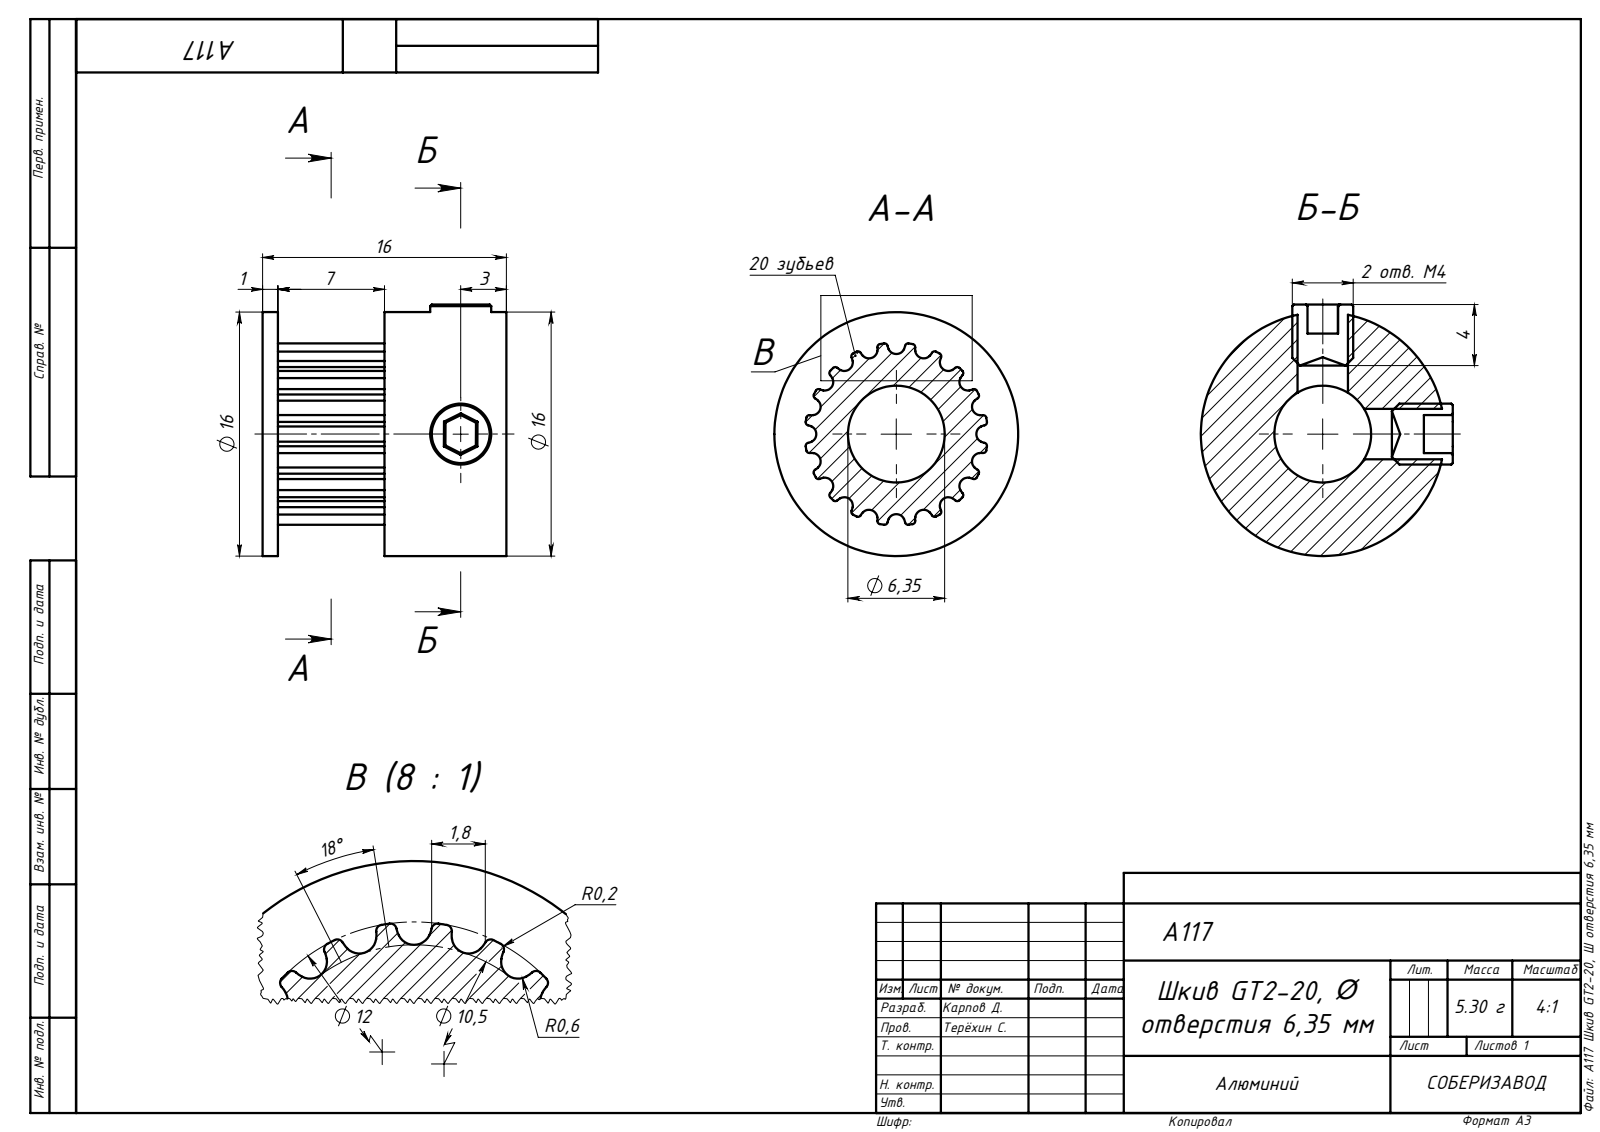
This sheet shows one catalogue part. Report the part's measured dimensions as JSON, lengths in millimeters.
{"part_name": "A117 Шкив GT2-20, O отверстия 6,35 мм", "step_written_by": "SolidWorks 2019 (AUTOMOTIVE_DESIGN)", "units": "millimeters", "bodies": {"solids": 3, "faces": 197, "planar": 32, "cylindrical": 153, "other": 12}, "overall_size": [16.54, 16.5, 16], "volume_mm3": 1989, "surface_area_mm2": 1917, "round_holes": [[3.3, 2], [6.35, 1]], "round_bosses_or_shafts": [[4, 2], [16, 1]], "partial_cylinders_radius": [[0.2, 40], [1, 40], [0.56, 20], [6, 1]], "face_to_face_distances": [8, 16, 1, 7, 15, 1.9, 2, 2.23, 2.24]}
